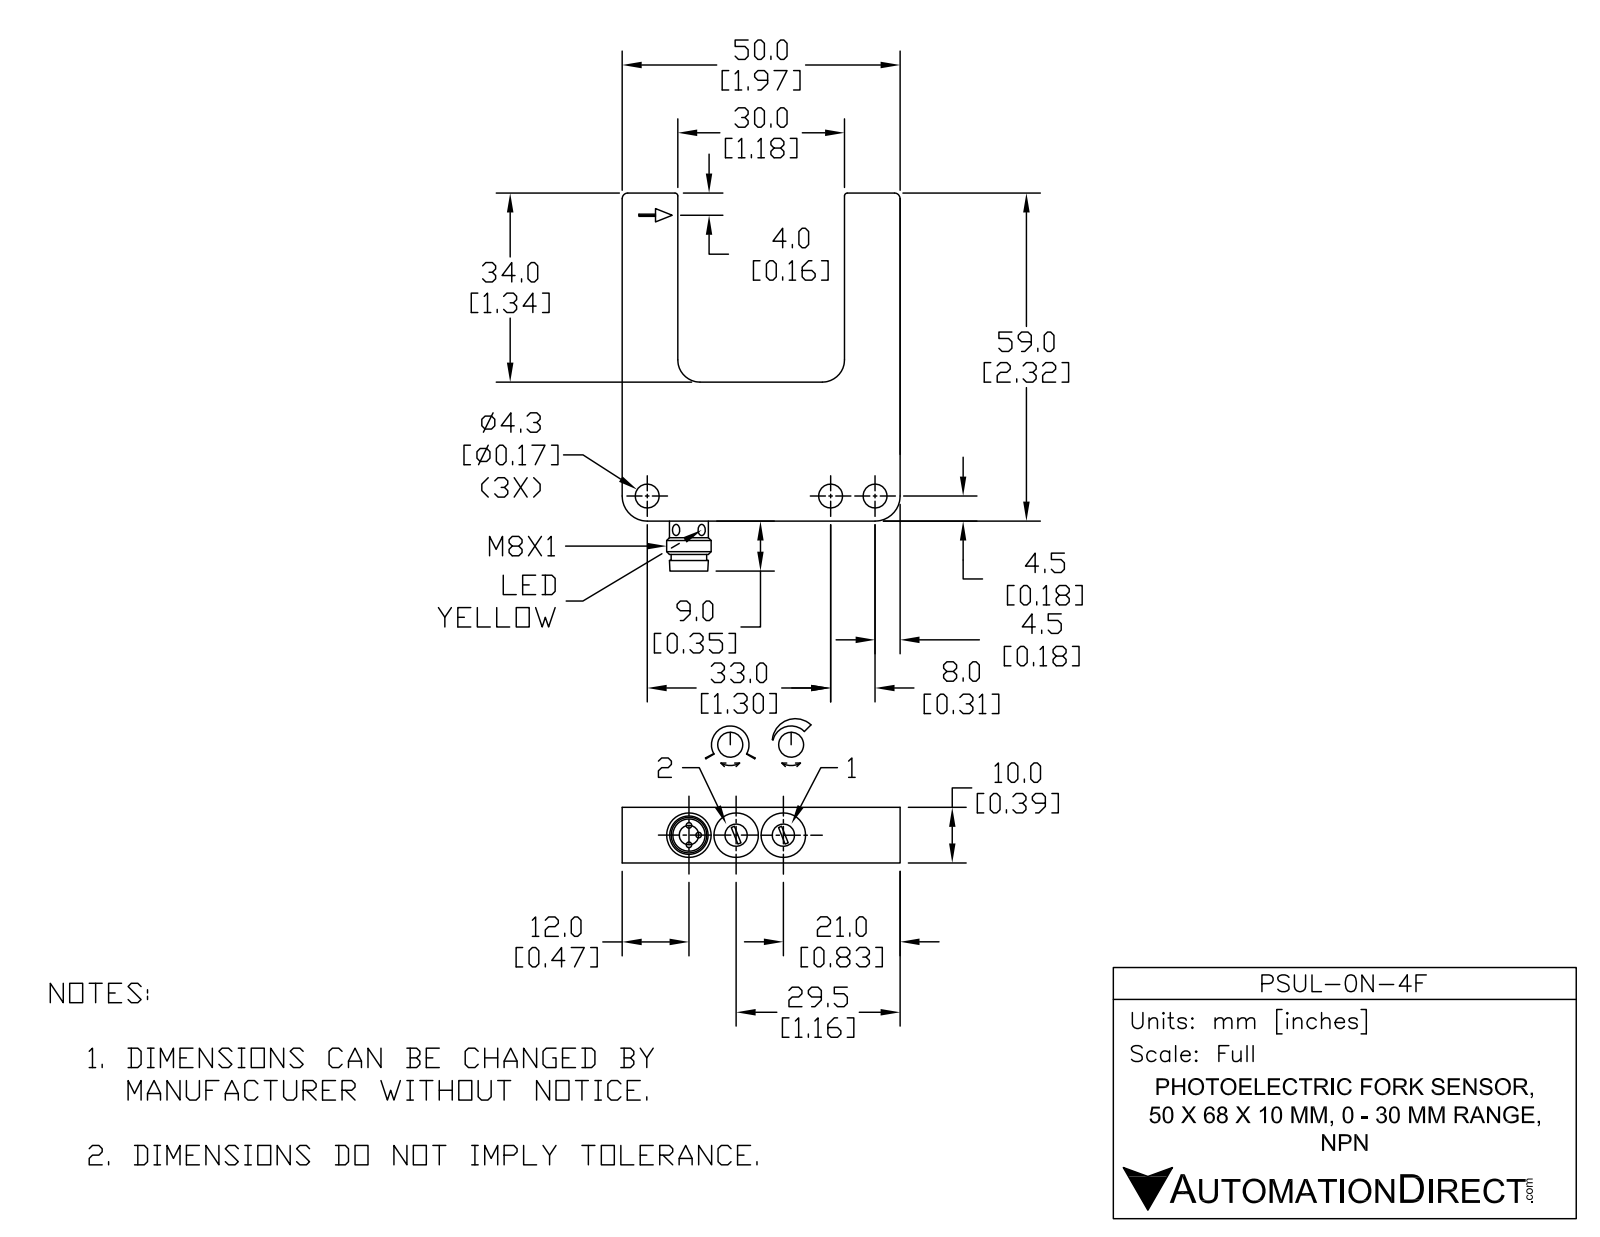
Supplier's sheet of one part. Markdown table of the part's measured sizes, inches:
| quantity | value |
| --- | --- |
| part name | PSUL-0N-4F |
| STEP written by | SolidWorks 2016 (AUTOMOTIVE_DESIGN) |
| units | inches |
| bodies | 1 solid, 83 faces (35 planar, 42 cylindrical, 6 other) |
| overall size | 2.677 × 1.969 × 0.394 |
| volume | 1.162 in³ |
| surface area | 11.28 in² |
| round holes (diameter × count) | 0.169 × 3, 0.079 × 2, 0.157 × 2, 0.315 × 2, 0.228 × 1 |
| round bosses / shafts (diameter × count) | 0.315 × 1, 0.267 × 1 |
| partial cylindrical surfaces (radius × count) | 0.02 × 2, 0.039 × 2, 0.063 × 2, 0.157 × 2, 0.177 × 2 |
| main face-to-face distances | 0.394, 1.575, 1.969, 1.181, 0.984, 1.339, 2.323, 2.319, 0.98, 0.157 |
| hole center spacings | 0.335, 0.315, 0.669, 1.299, 1.614 |
